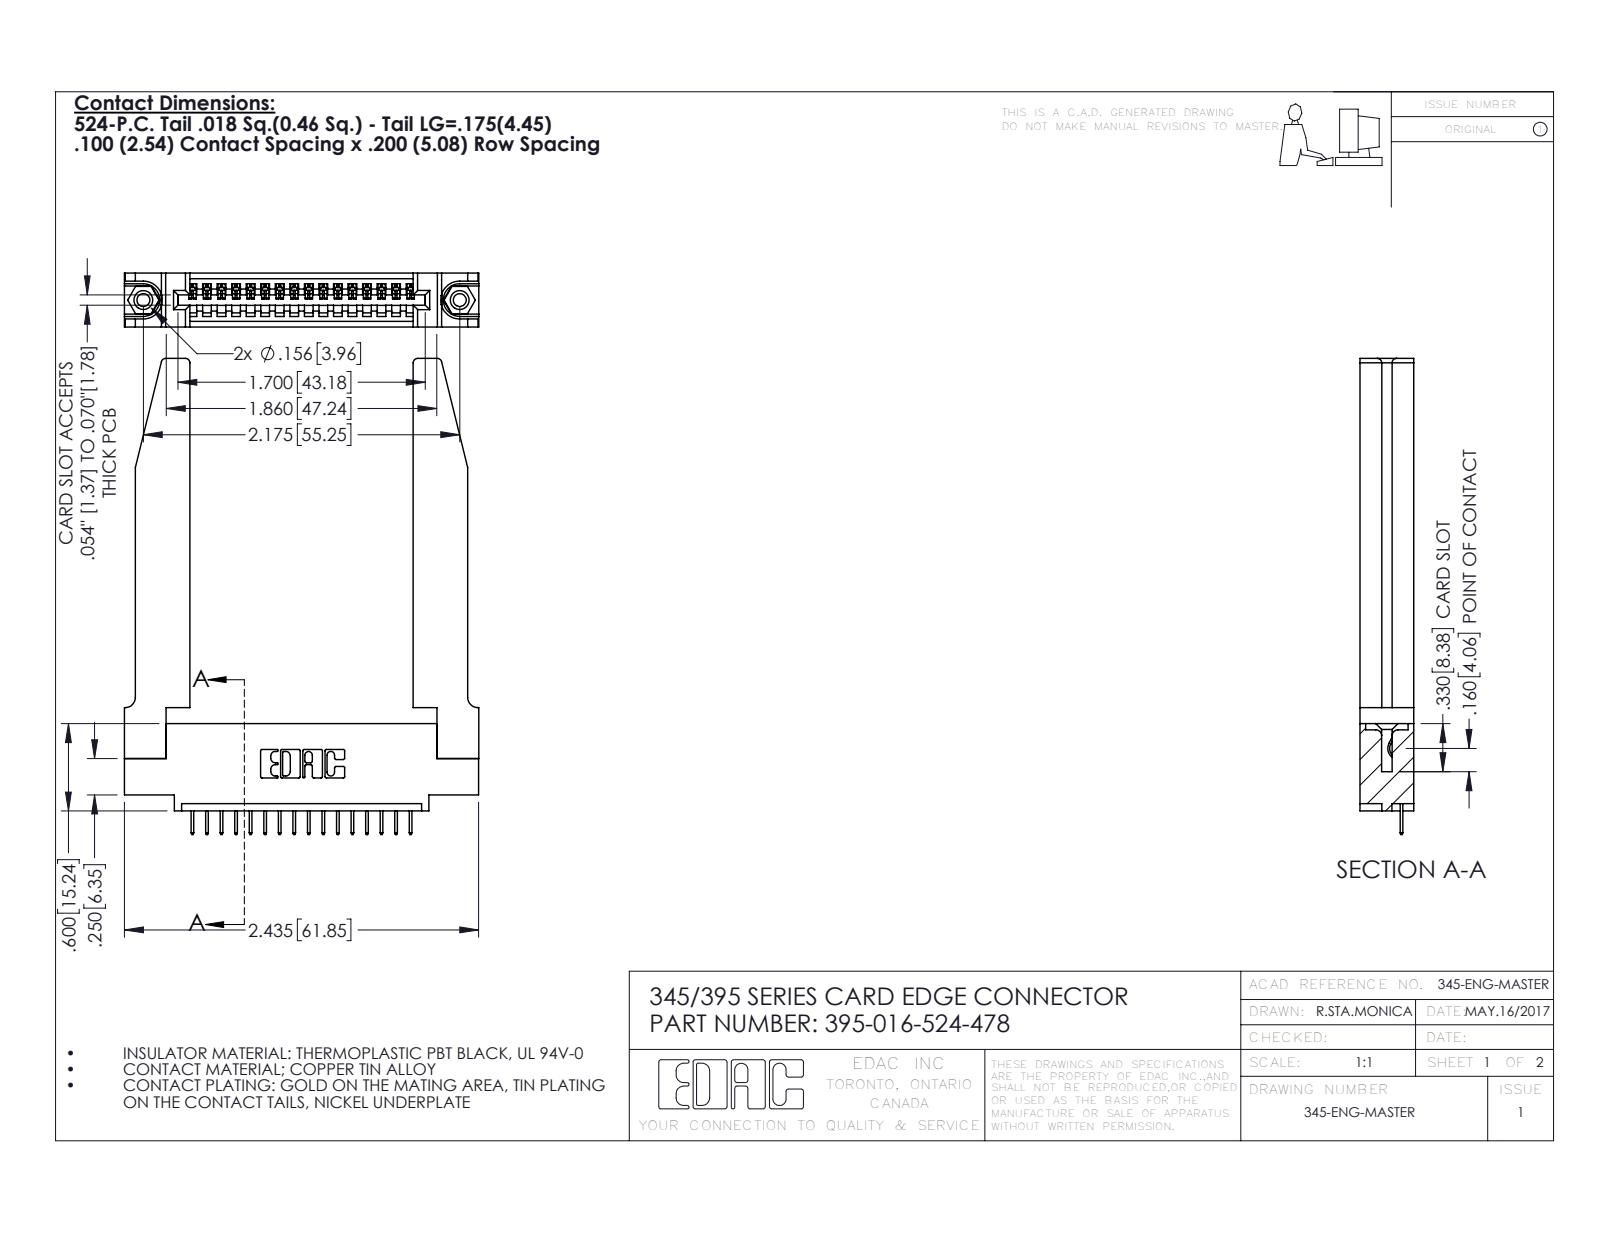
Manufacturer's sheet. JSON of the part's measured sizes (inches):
{"part_name": "395-016-524-478; 345-220-078_345-220-078; 345 Part_0.110 Offset - 0.156 Dia-TH; 345-292-001_345-293-124 (+1 more)", "step_written_by": "SolidWorks 2016 (CONFIG_CONTROL_DESIGN)", "units": "inches", "bodies": {"solids": 21, "faces": 1356, "planar": 962, "cylindrical": 342, "other": 52}, "overall_size": [3.272, 2.436, 0.37], "volume_in3": 0.811, "surface_area_in2": 21.26, "round_holes": [[0.089, 2], [0.125, 2], [0.156, 2], [0.064, 1]], "round_bosses_or_shafts": [[0.155, 2]], "partial_cylinders_radius": [[0.006, 32], [0.01, 22], [0.03, 8], [0.007, 6], [0.031, 6], [0.026, 3], [0.031, 2], [0.04, 2]], "face_to_face_distances": [0.37, 0.072, 0.298, 0.148, 0.15, 0.22, 0.077, 0.2, 1.535, 0.098], "hole_center_spacings": [0.27, 1.942, 2.175]}
